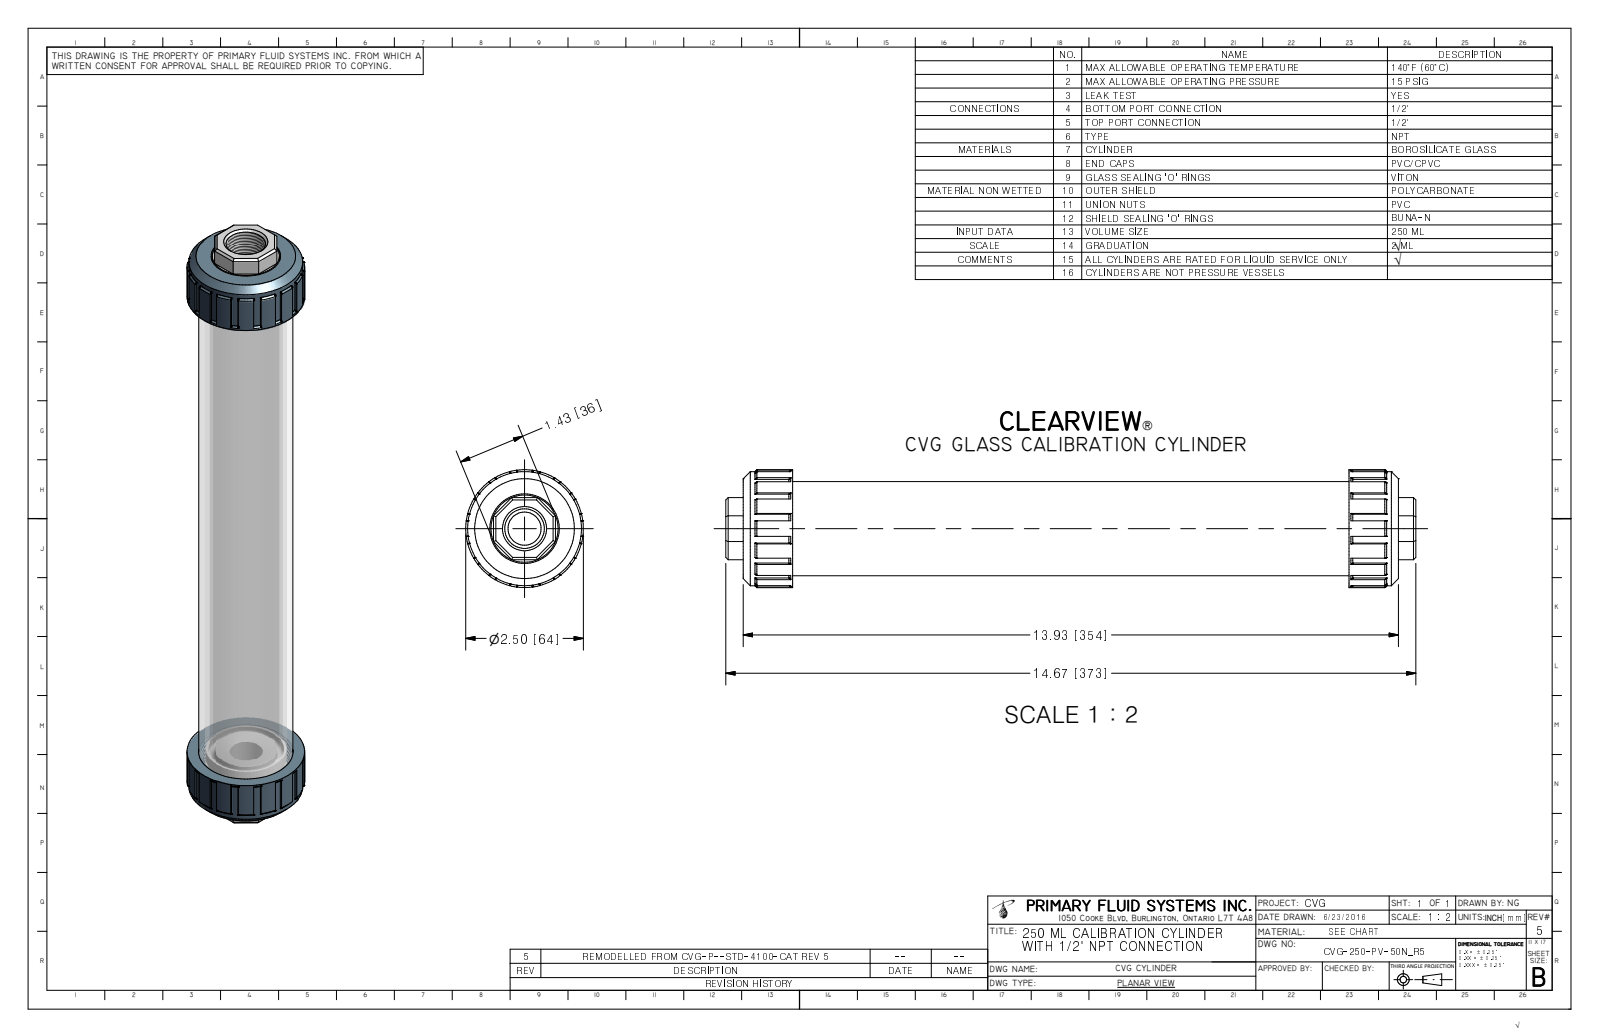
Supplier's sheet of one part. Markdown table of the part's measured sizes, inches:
| quantity | value |
| --- | --- |
| part name | CVG-250-PVC-50N_R5; CVG-3-250-POLY-NPT-50_R11; CVG-6-250_R0; CVG-1-250-A_R0 (+1 more) |
| STEP written by | Autodesk Inventor 2009 (AUTOMOTIVE_DESIGN) |
| units | inches |
| bodies | 6 solids, 322 faces (101 planar, 33 cylindrical, 188 other) |
| overall size | 14.67 × 2.5 × 2.5 |
| volume | 21.42 in³ |
| surface area | 348.5 in² |
| round holes (diameter × count) | 0.703 × 1, 1.417 × 1, 1.631 × 1, 1.75 × 1 |
| round bosses / shafts (diameter × count) | 2.5 × 1, 2 × 1, 1.921 × 1, 1.857 × 1, 1.721 × 1, 1.587 × 1, 1.575 × 1, 1.427 × 1 |
| main face-to-face distances | 0.82, 12.65, 11.83, 1.318, 0.269, 13.201, 0.551, 12.381, 0.6, 0.869 |
